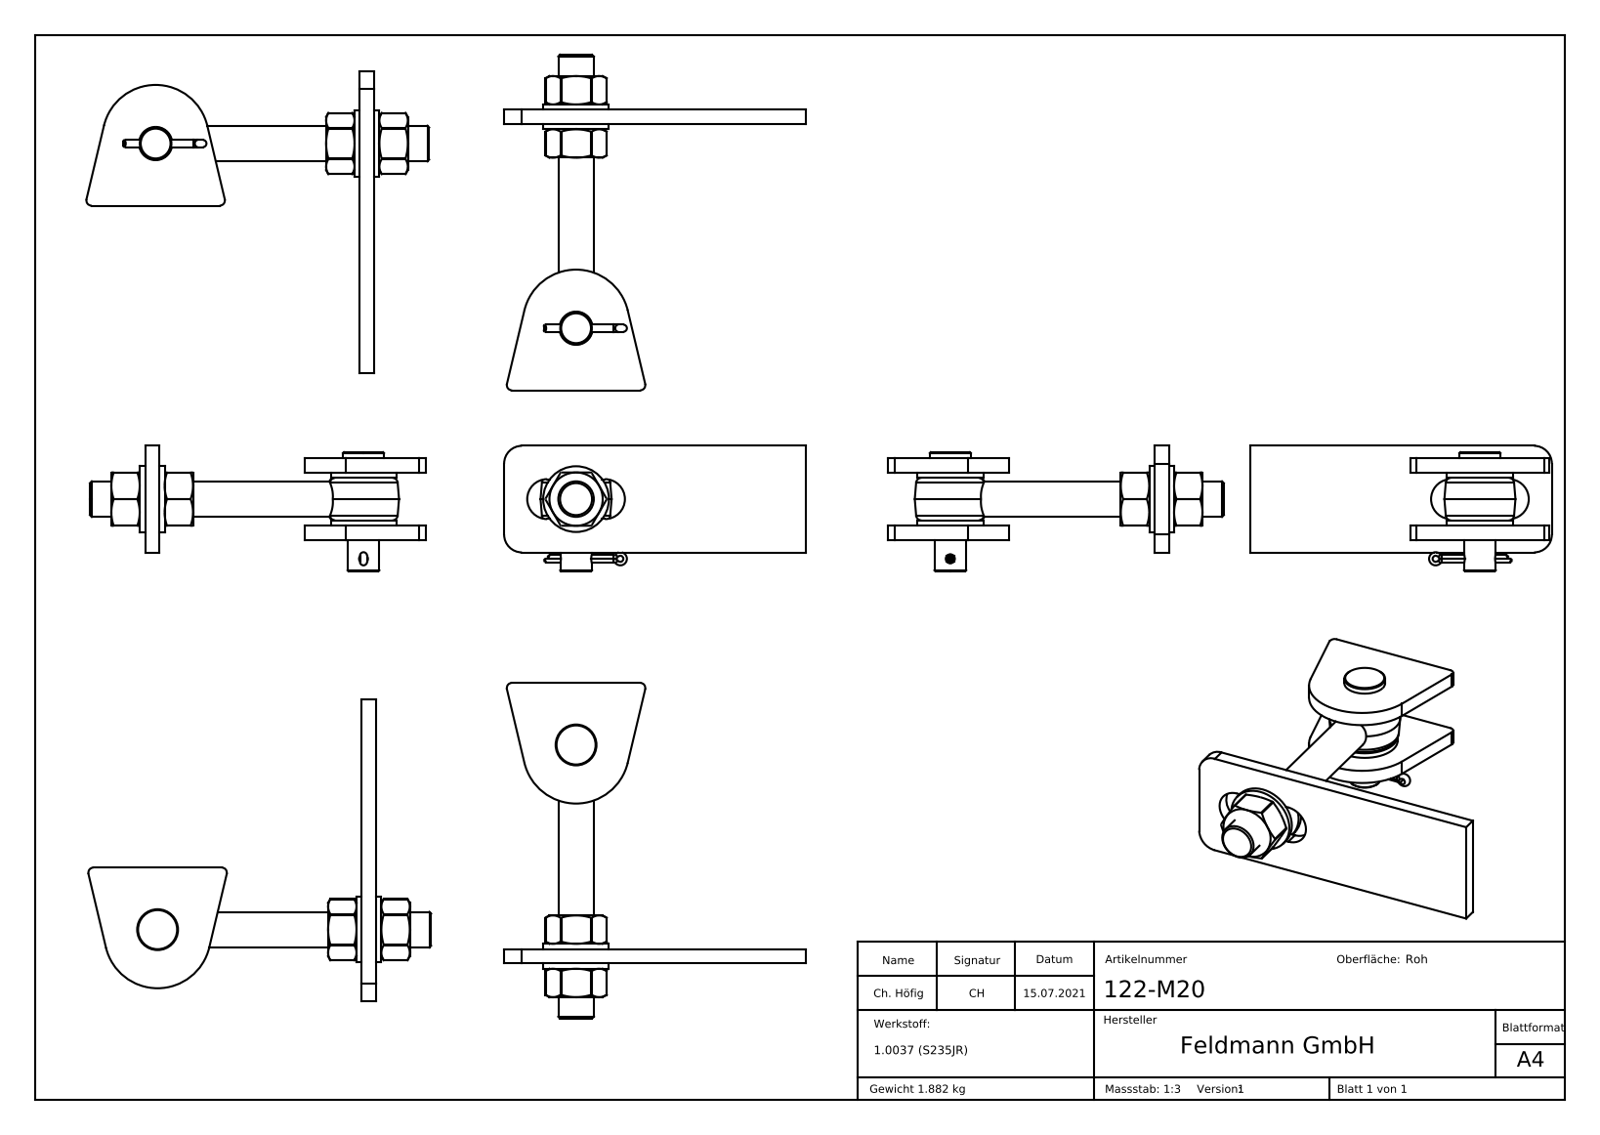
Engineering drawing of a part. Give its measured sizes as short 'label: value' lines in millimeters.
name: DIN 934 M4-M20_DIN 934 M20; Torband Teil4; DIN 934 M4-M20; Splint DIN94 - ISO 1234 Konfig_DIN 94 4x40 (+8 more)
written by: SolidWorks 2018 (CONFIG_CONTROL_DESIGN)
unit: mm
bodies: 12 solids, 407 faces (173 planar, 85 cylindrical, 149 other)
size: 24000 × 14000 × 14000
volume: 241 014 mm³; area: 78 049 mm²
holes: 2× ⌀21, 1× ⌀5, 1× ⌀17.5, 1× ⌀18.2, 1× ⌀18.7
bosses: 2× ⌀37, 1× ⌀23, 1× ⌀20, 1× ⌀17.8, 1× ⌀4
rounds: 6× R0.5, 2× R1, 2× R2.99, 2× R3, 2× R10, 2× R11.25, 1× R1.71, 1× R9.2
face distances: 8, 38, 30, 11, 3, 46, 27, 42, 35, 7
